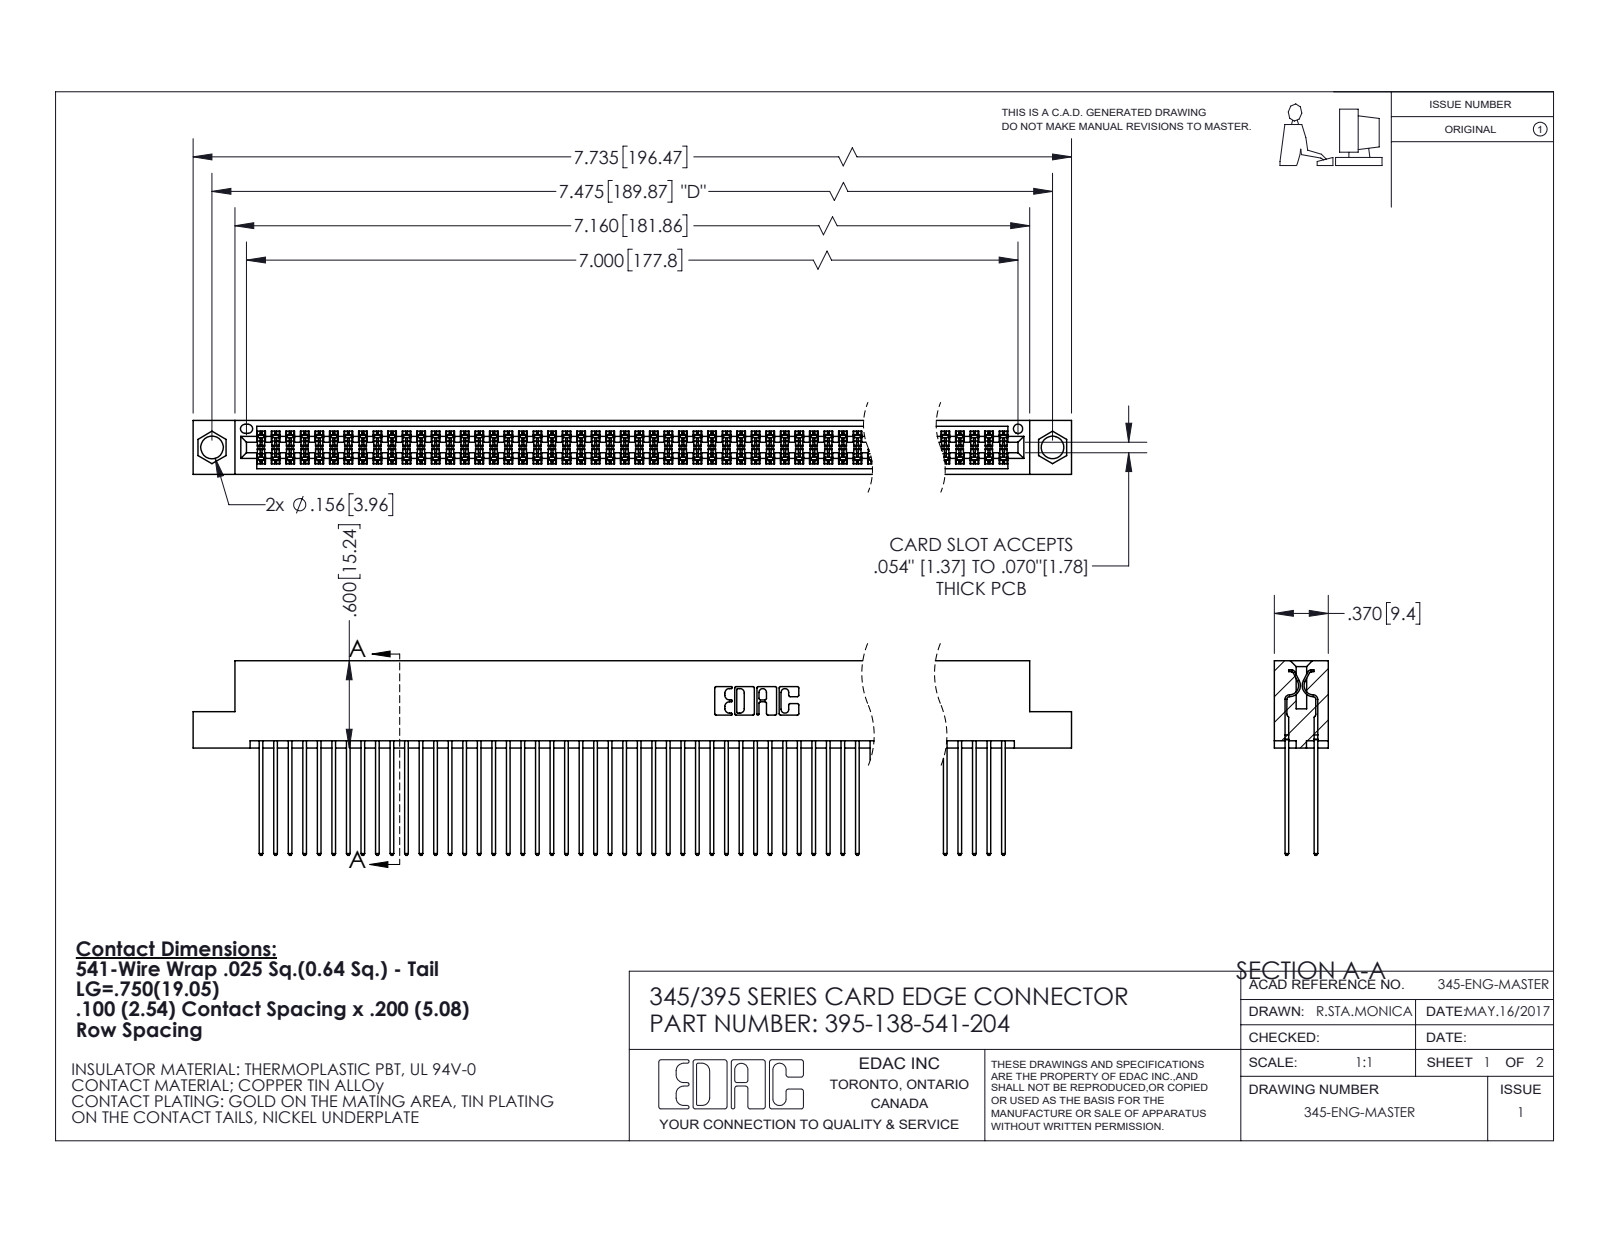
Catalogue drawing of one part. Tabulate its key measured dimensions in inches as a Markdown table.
| quantity | value |
| --- | --- |
| part name | 345 Part_Flush Mounting Lugs - 0.156 Dia-TI; 345-292-001_345-293-141; 395-138-541-204 |
| STEP written by | SolidWorks 2020 (CONFIG_CONTROL_DESIGN) |
| units | inches |
| bodies | 139 solids, 7040 faces (4648 planar, 2392 cylindrical, 0 other) |
| overall size | 7.735 × 1.337 × 0.37 |
| volume | 1.222 in³ |
| surface area | 52.22 in² |
| round holes (diameter × count) | 0.156 × 2, 0.064 × 1 |
| partial cylindrical surfaces (radius × count) | 0.006 × 207, 0.01 × 138, 0.01 × 22, 0.007 × 6, 0.031 × 6, 0.026 × 3, 0.014 × 2, 0.019 × 2 |
| main face-to-face distances | 0.072, 0.298, 0.2, 0.098, 0.272, 0.025, 0.225, 0.37, 0.175, 0.149 |
| hole center spacings | 0.27, 7.239, 7.475 |
